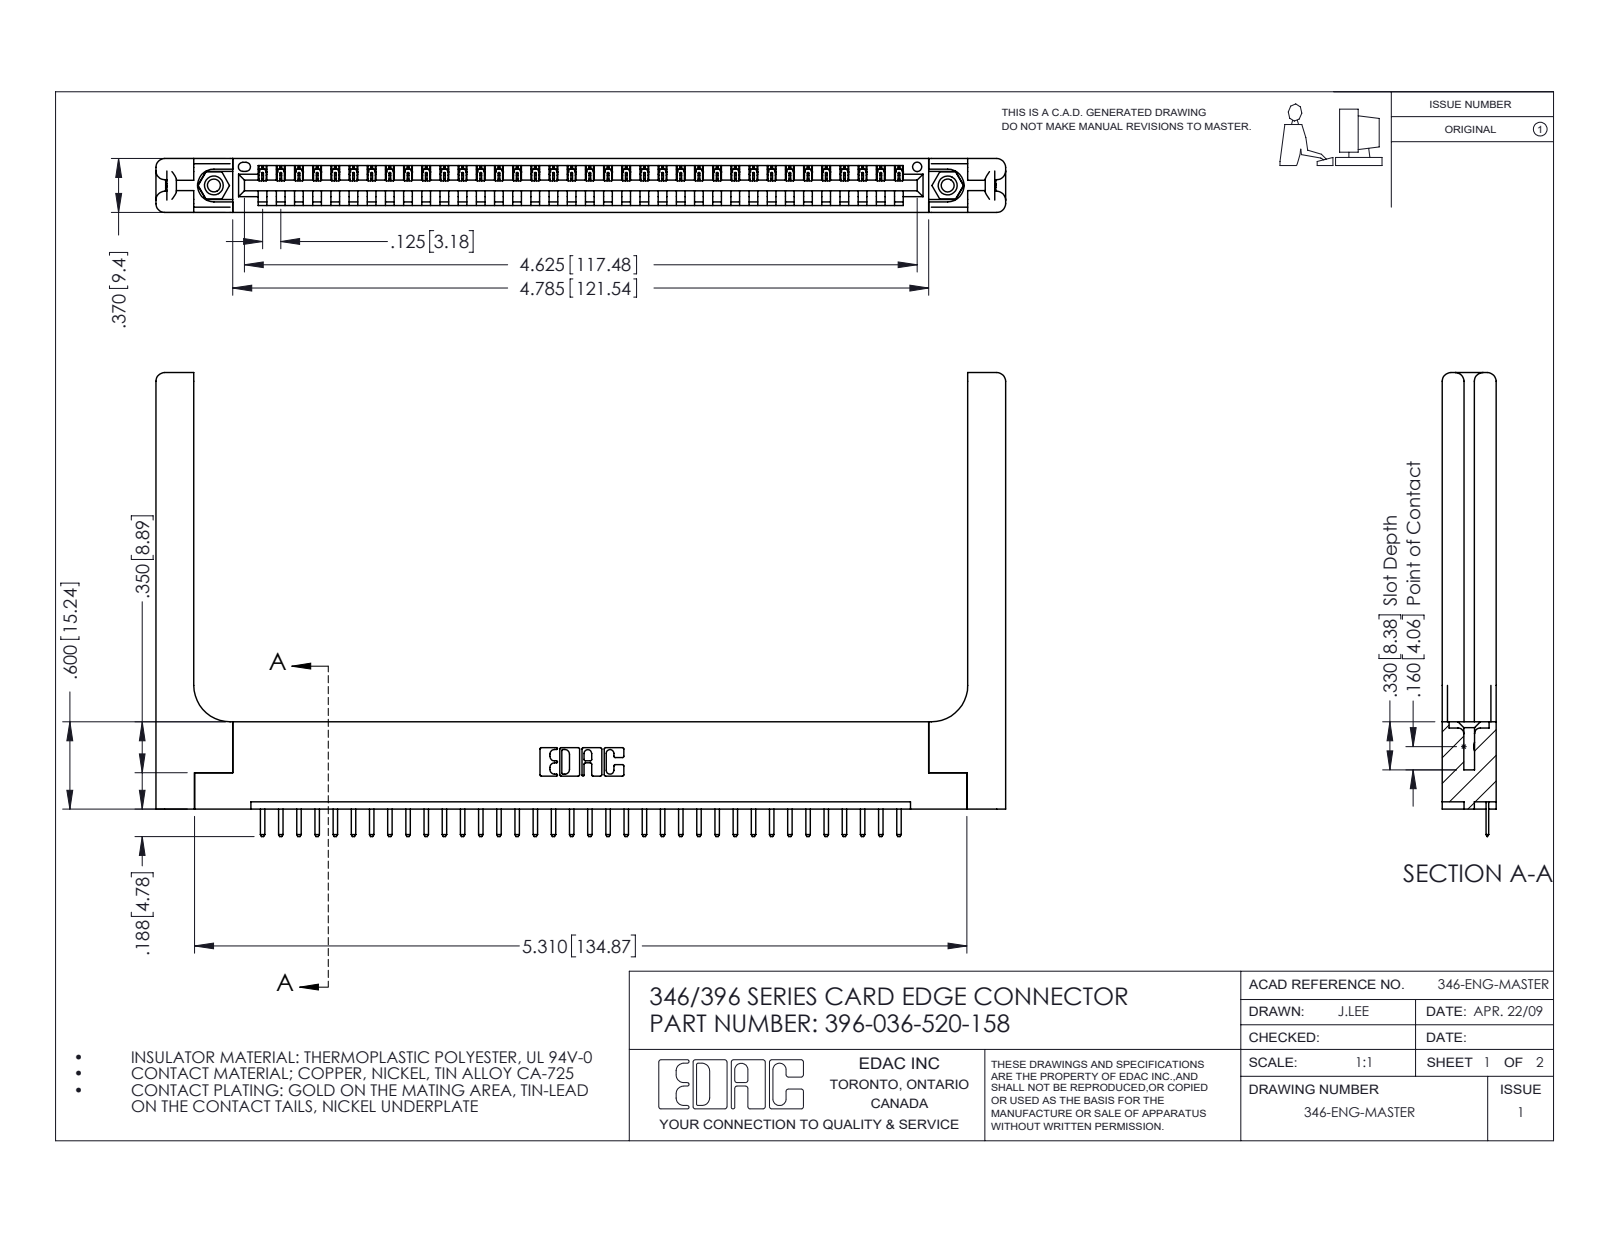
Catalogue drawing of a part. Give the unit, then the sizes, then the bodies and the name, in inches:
Units: inches
Overall size (bounding box): 5.841 × 3.188 × 0.37
Round holes (diameter × count): ⌀0.089 ×2, ⌀0.125 ×2, ⌀0.156 ×2, ⌀0.064 ×1
Round bosses / shafts (diameter × count): ⌀0.155 ×2
Partial cylindrical surfaces — rounded edges, fillets, slot ends (radius × count): R0.01 ×74, R0.006 ×72, R0.01 ×22, R0.06 ×16, R0.007 ×6, R0.031 ×6, R0.026 ×3, R0.03 ×2
Main face-to-face distances: 0.37, 0.048, 0.322, 0.072, 0.148, 0.15, 0.25, 0.298, 0.025, 0.222
Hole centre spacings: 0.246, 4.836, 5.045
Volume: 1.317 in³ · Surface area: 34.61 in²
Bodies: 41 solids, 2610 faces (1736 planar, 814 cylindrical, 60 other)
Part name (STEP PRODUCT): 345-292-001_345-293-120; 345-250-001_345-250-001-102; 396-036-520-158; 346-220-058_345-220-058 (+1 more)
STEP written by: SolidWorks 2016 (CONFIG_CONTROL_DESIGN)
